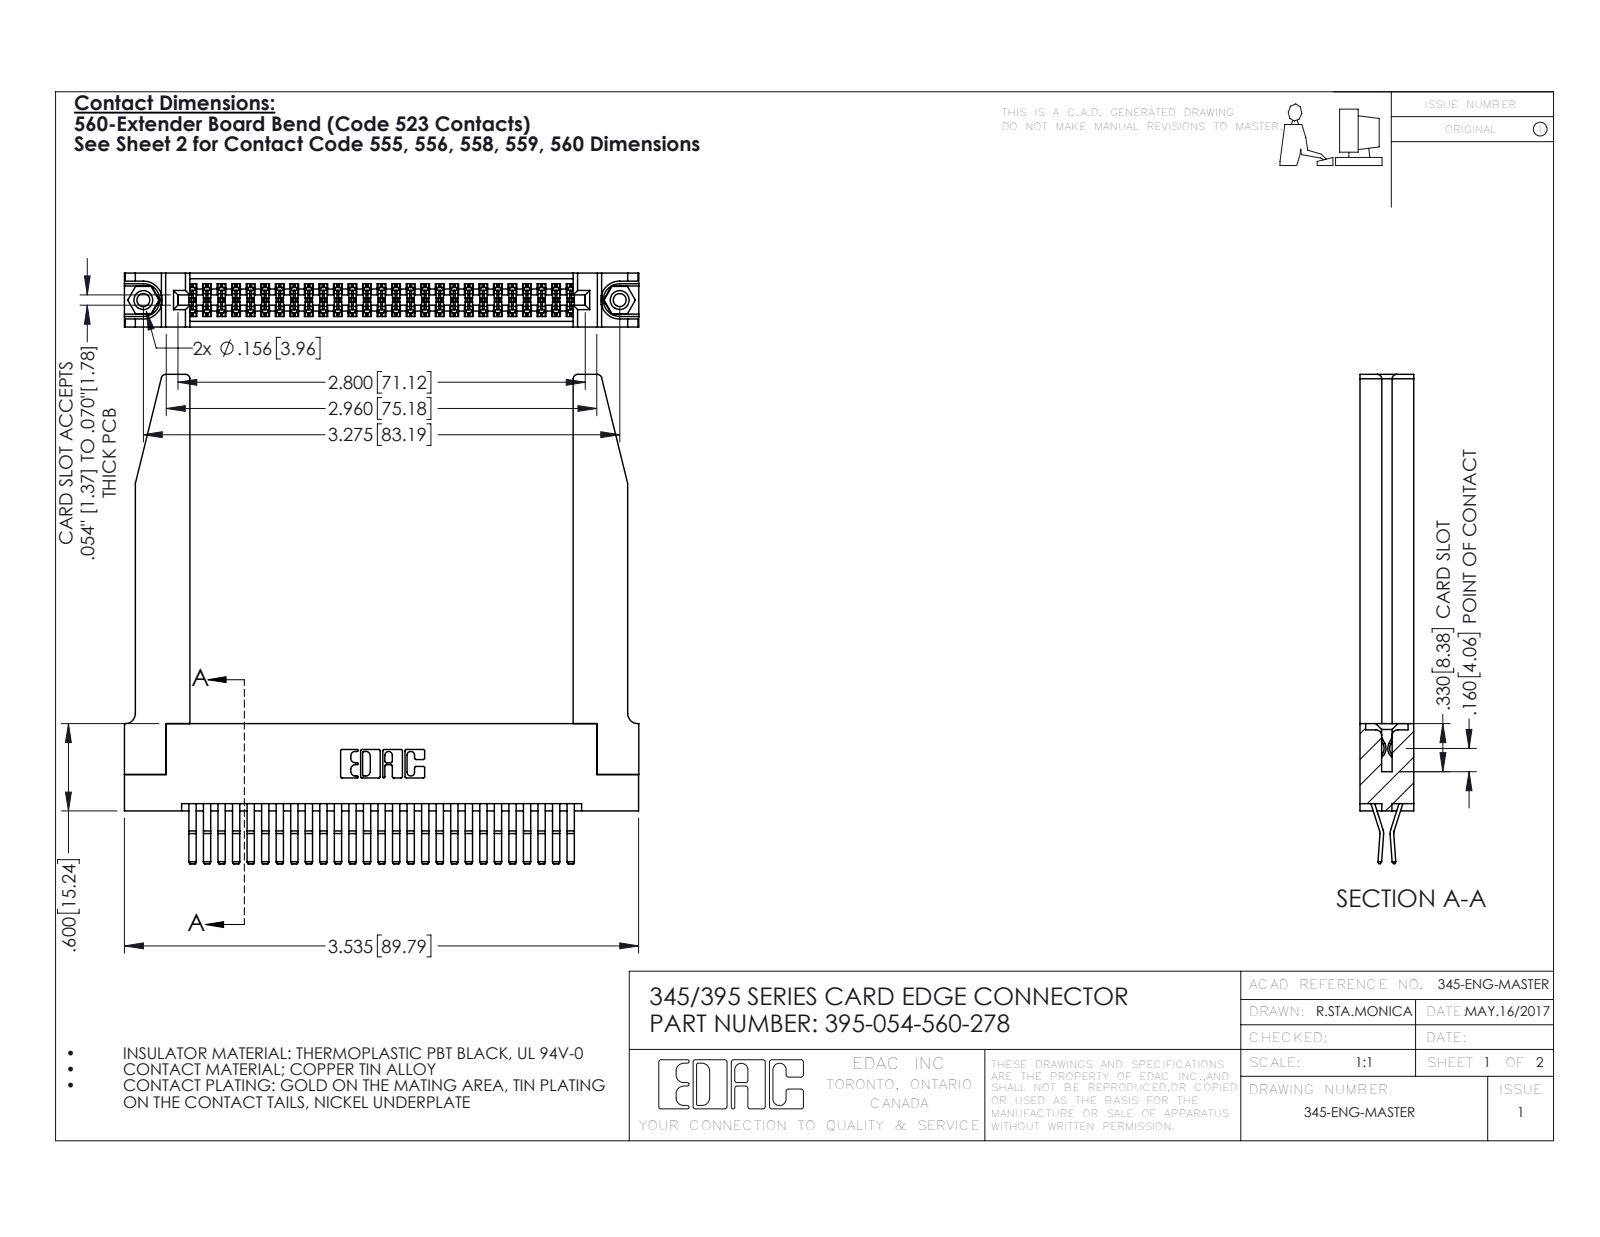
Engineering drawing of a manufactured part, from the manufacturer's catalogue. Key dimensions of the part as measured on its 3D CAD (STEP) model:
Part name (STEP PRODUCT): 395-054-560-278; 345-220-078_345-220-078; 345-250-001_345-250-001-102; 345-292-001_560 Tail (+1 more)
STEP written by: SolidWorks 2016 (CONFIG_CONTROL_DESIGN)
Units: inches
Bodies: 59 solids, 3168 faces (2004 planar, 1112 cylindrical, 52 other)
Overall size (bounding box): 3.536 × 3.362 × 0.37
Volume: 1.02 in³ · Surface area: 32.04 in²
Round holes (diameter × count): ⌀0.089 ×2, ⌀0.125 ×2, ⌀0.156 ×2, ⌀0.064 ×1
Round bosses / shafts (diameter × count): ⌀0.155 ×2
Partial cylindrical surfaces — rounded edges, fillets, slot ends (radius × count): R0.006 ×81, R0.01 ×22, R0.03 ×8, R0.007 ×6, R0.031 ×6, R0.026 ×3, R0.01 ×2, R0.014 ×2
Main face-to-face distances: 0.37, 0.072, 0.298, 0.025, 0.2, 0.098, 0.272, 0.225, 0.148, 0.15
Hole centre spacings: 0.27, 3.04, 3.275
